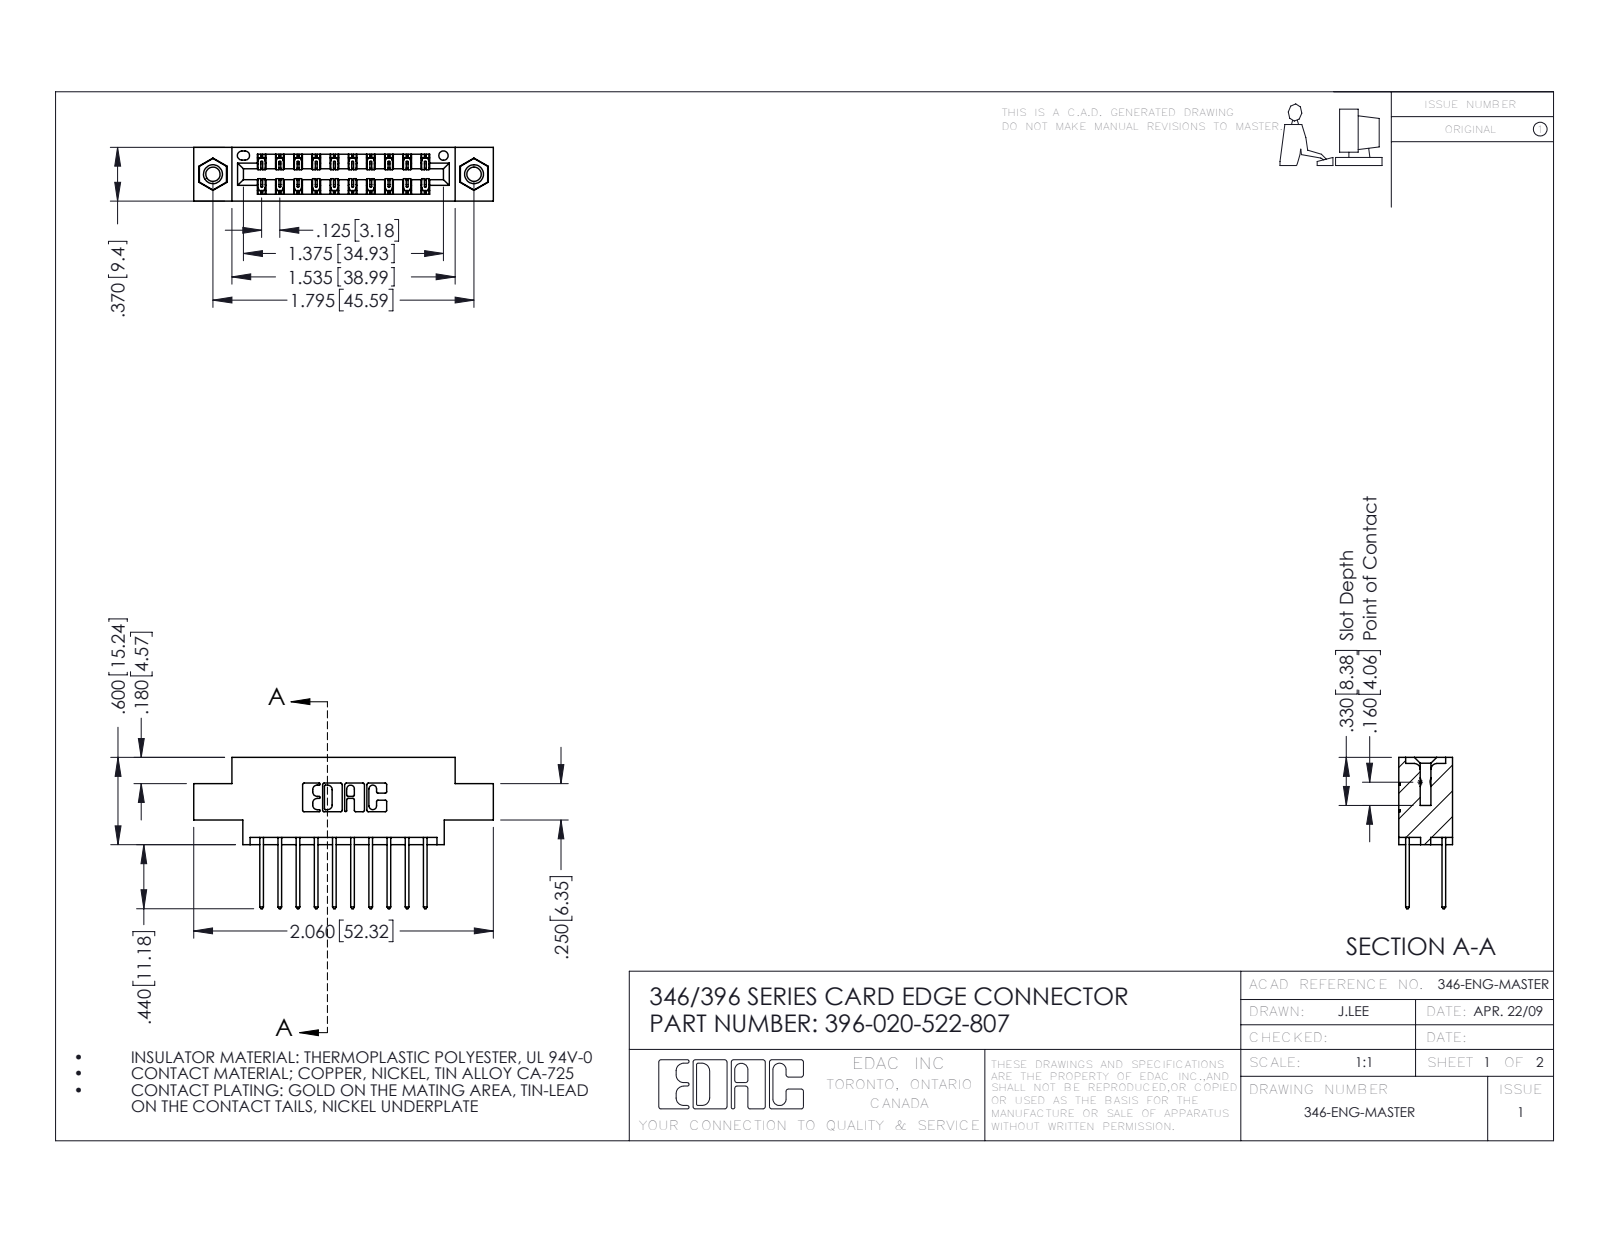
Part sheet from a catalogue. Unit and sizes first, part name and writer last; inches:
Units: inches
Overall size (bounding box): 2.06 × 1.04 × 0.37
Round holes (diameter × count): ⌀0.098 ×2, ⌀0.125 ×2, ⌀0.156 ×2, ⌀0.064 ×1
Round bosses / shafts (diameter × count): ⌀0.155 ×2
Partial cylindrical surfaces — rounded edges, fillets, slot ends (radius × count): R0.006 ×30, R0.01 ×22, R0.01 ×20, R0.007 ×6, R0.031 ×6, R0.026 ×3, R0.014 ×2, R0.022 ×2
Main face-to-face distances: 0.25, 0.048, 0.322, 0.37, 0.072, 0.298, 0.025, 0.275, 0.222, 0.148
Hole centre spacings: 0.246, 1.59, 1.795
Volume: 0.289 in³ · Surface area: 10.01 in²
Bodies: 23 solids, 1226 faces (812 planar, 398 cylindrical, 16 other)
Part name (STEP PRODUCT): 345-250-001_345-250-005-103; 396-020-522-807; 345-292-001_345-293-122; 346 Part_0.170 Offset - 0.156 Dia-TI
STEP written by: SolidWorks 2016 (CONFIG_CONTROL_DESIGN)
